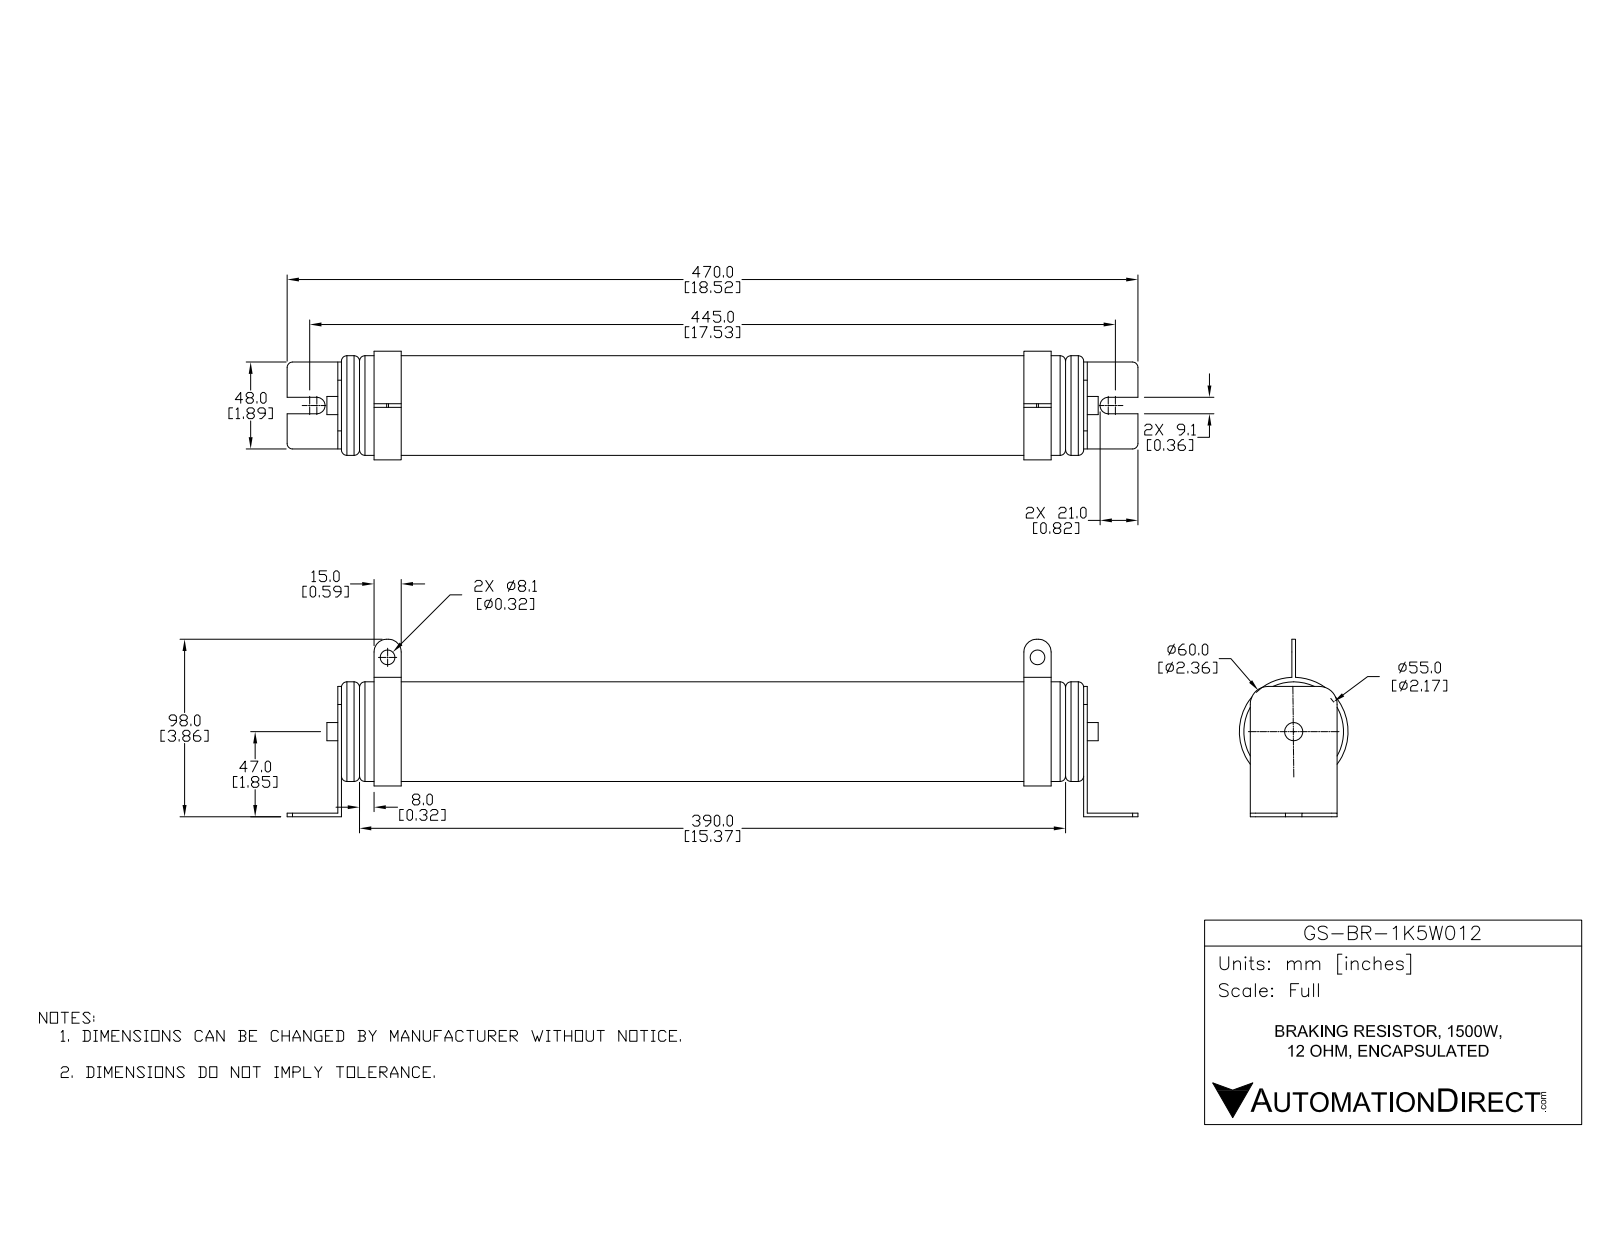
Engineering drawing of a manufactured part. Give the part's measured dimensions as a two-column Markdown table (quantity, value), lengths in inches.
| quantity | value |
| --- | --- |
| part name | GS-BR-1K5W012 |
| STEP written by | SolidWorks 2015 (AUTOMOTIVE_DESIGN) |
| units | inches |
| bodies | 2 solids, 91 faces (41 planar, 38 cylindrical, 12 other) |
| overall size | 18.504 × 3.858 × 2.362 |
| volume | 61.39 in³ |
| surface area | 143.2 in² |
| round holes (diameter × count) | 0.319 × 2 |
| round bosses / shafts (diameter × count) | 2.362 × 1, 2.166 × 1, 2.165 × 1, 0.394 × 1 |
| partial cylindrical surfaces (radius × count) | 0.118 × 4, 0.276 × 4, 0.179 × 2, 0.394 × 2 |
| main face-to-face distances | 0.079, 16.299, 16.22, 16.142, 1.378, 14.921, 1.299, 14.843, 0.787, 15.512 |
| hole center spacings | 14.134 |
